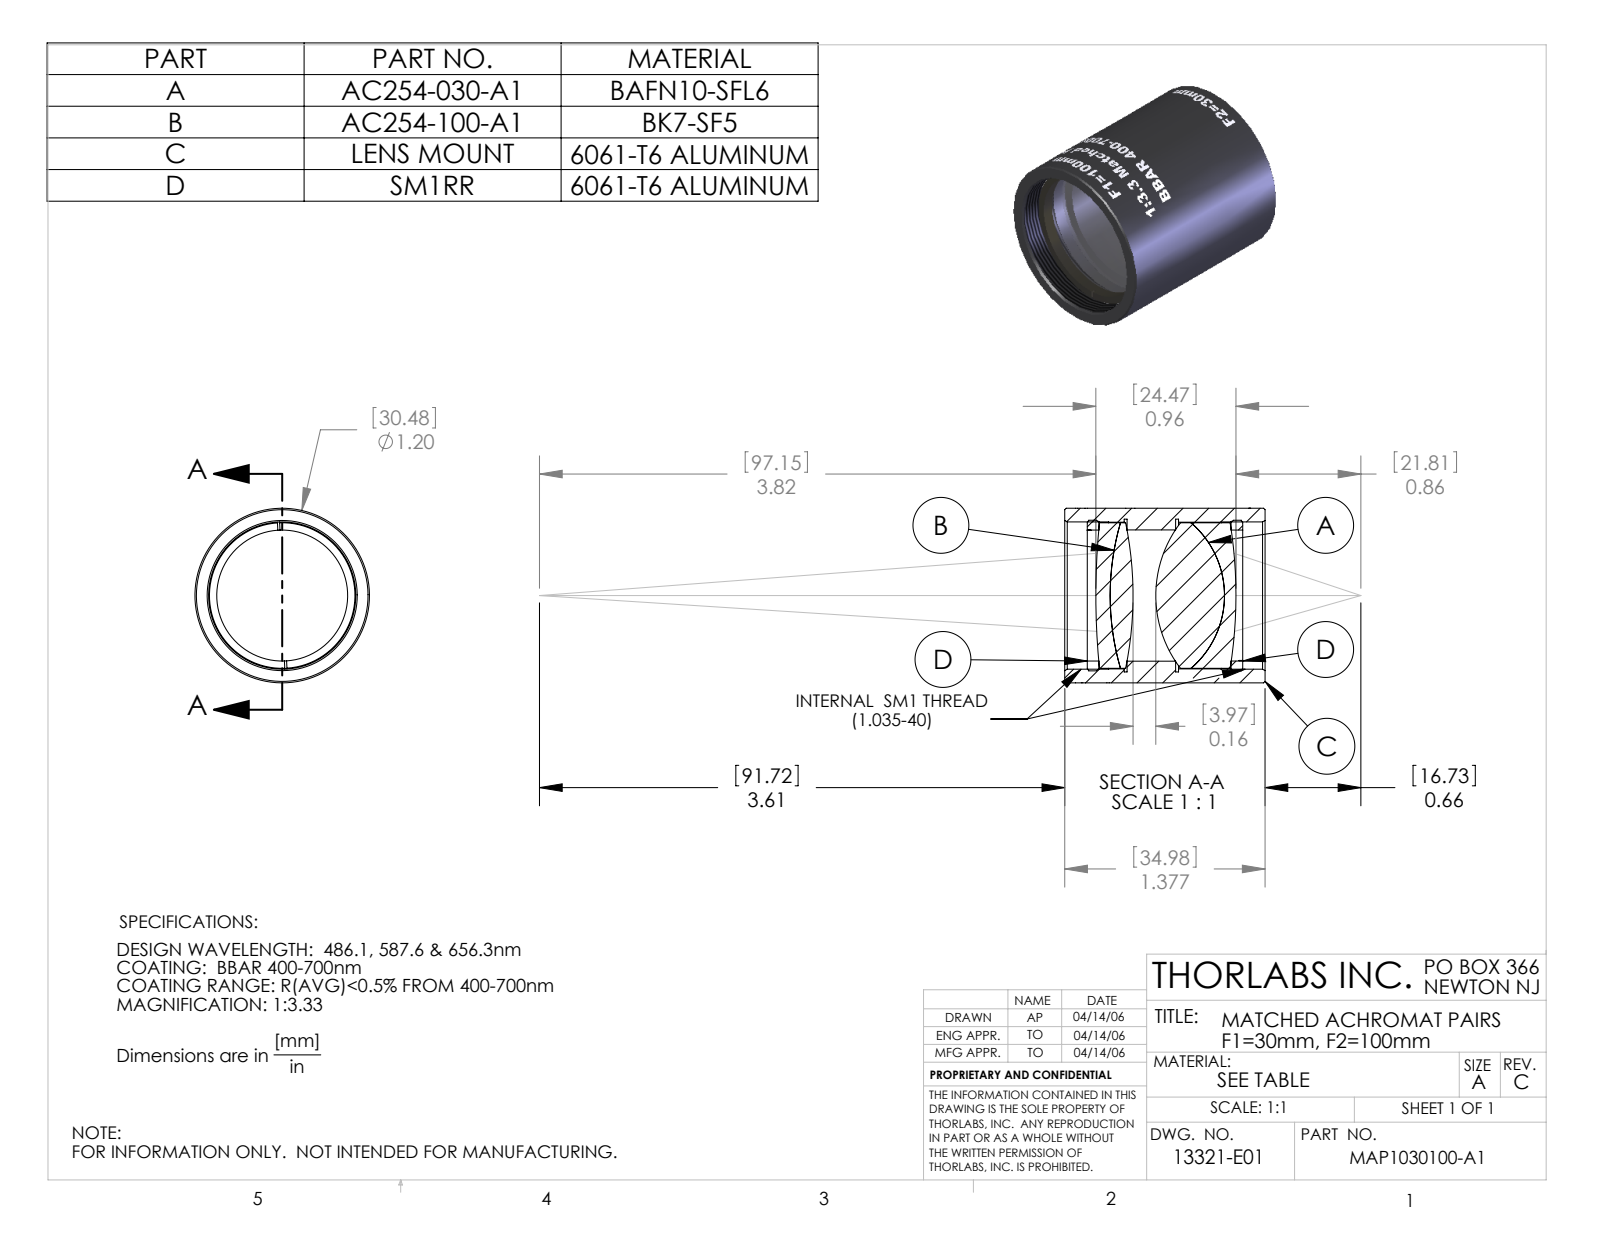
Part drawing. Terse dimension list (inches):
name: 13321-E0W
written by: SolidWorks 2007 (AUTOMOTIVE_DESIGN)
unit: in
bodies: 7 solids, 189 faces (24 planar, 135 cylindrical, 30 other)
size: 1.377 × 1.2 × 1.2
volume: 1.06 in³; area: 20.71 in²
holes: 1× ⌀0.9, 1× ⌀0.902, 1× ⌀1.008, 1× ⌀1.012, 1× ⌀1.05
bosses: 1× ⌀1.2, 1× ⌀1.035, 1× ⌀1
face distances: 0.08, 0.989, 1.378, 0.949, 0.429, 0.615, 0.333, 0.762, 1.143, 0.527
